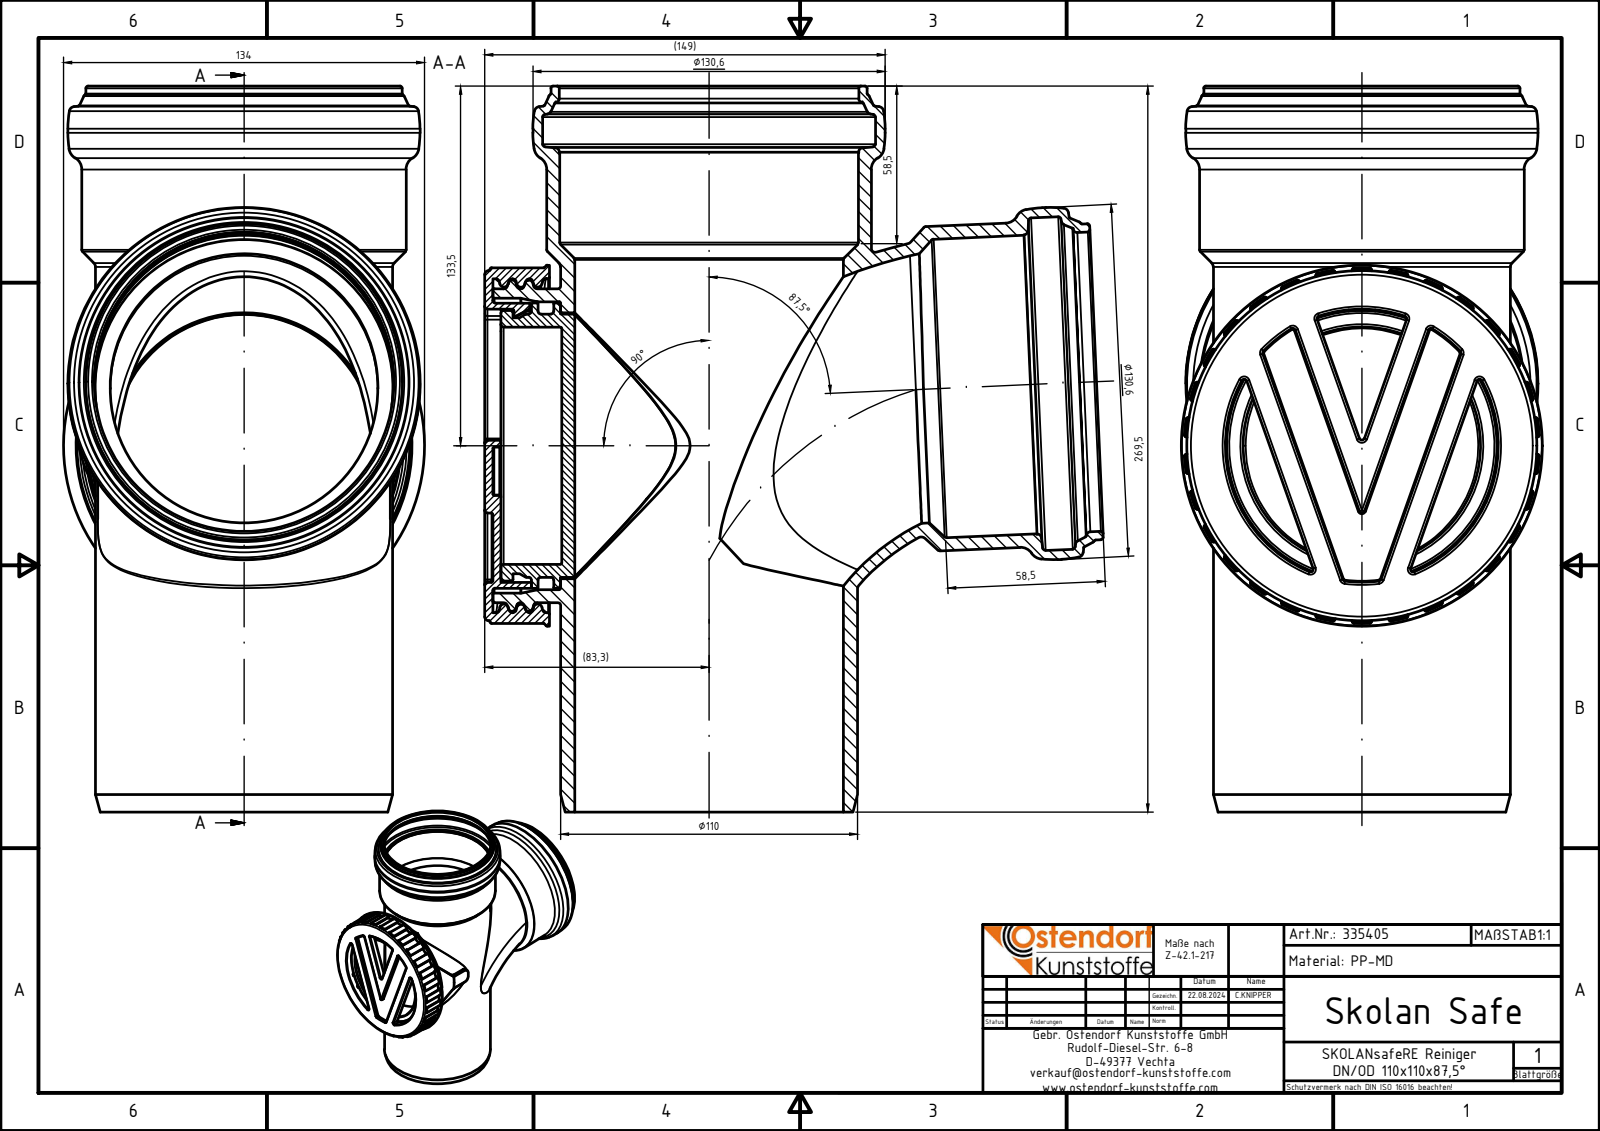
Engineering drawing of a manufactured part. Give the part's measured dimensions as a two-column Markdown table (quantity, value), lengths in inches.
| quantity | value |
| --- | --- |
| part name | 335405z; 335405 Skolan Safe-RE Reiniger DN_OD 110; Zusammenbau Einsatz und Deckel; 335600_1 Innteil für Reiniger DN_OD 110 (+1 more) |
| STEP written by | Autodesk Inventor 2024 (AUTOMOTIVE_DESIGN) |
| units | inches |
| bodies | 3 solids, 1239 faces (187 planar, 370 cylindrical, 682 other) |
| overall size | 11.356 × 9.71 × 5.478 |
| volume | 49.64 in³ |
| surface area | 577.8 in² |
| round holes (diameter × count) | 4.378 × 4, 4.366 × 2, 4.866 × 2, 3.469 × 1, 3.886 × 1, 3.925 × 1, 3.992 × 1, 4.209 × 1, 4.311 × 1, 4.882 × 1 |
| round bosses / shafts (diameter × count) | 3.846 × 3, 5.15 × 2, 4.744 × 2, 4.622 × 2, 4.169 × 2, 5.276 × 1, 5.118 × 1, 4.587 × 1 |
| partial cylindrical surfaces (radius × count) | 0.024 × 128, 0.012 × 72, 0.039 × 32, 0.02 × 25, 0.197 × 8, 0.016 × 6, 0.047 × 6, 0.079 × 6 |
| main face-to-face distances | 0.118, 0.119, 0.237, 0.098, 0.709, 0.827, 0.828, 0.946, 0.327, 0.563 |
